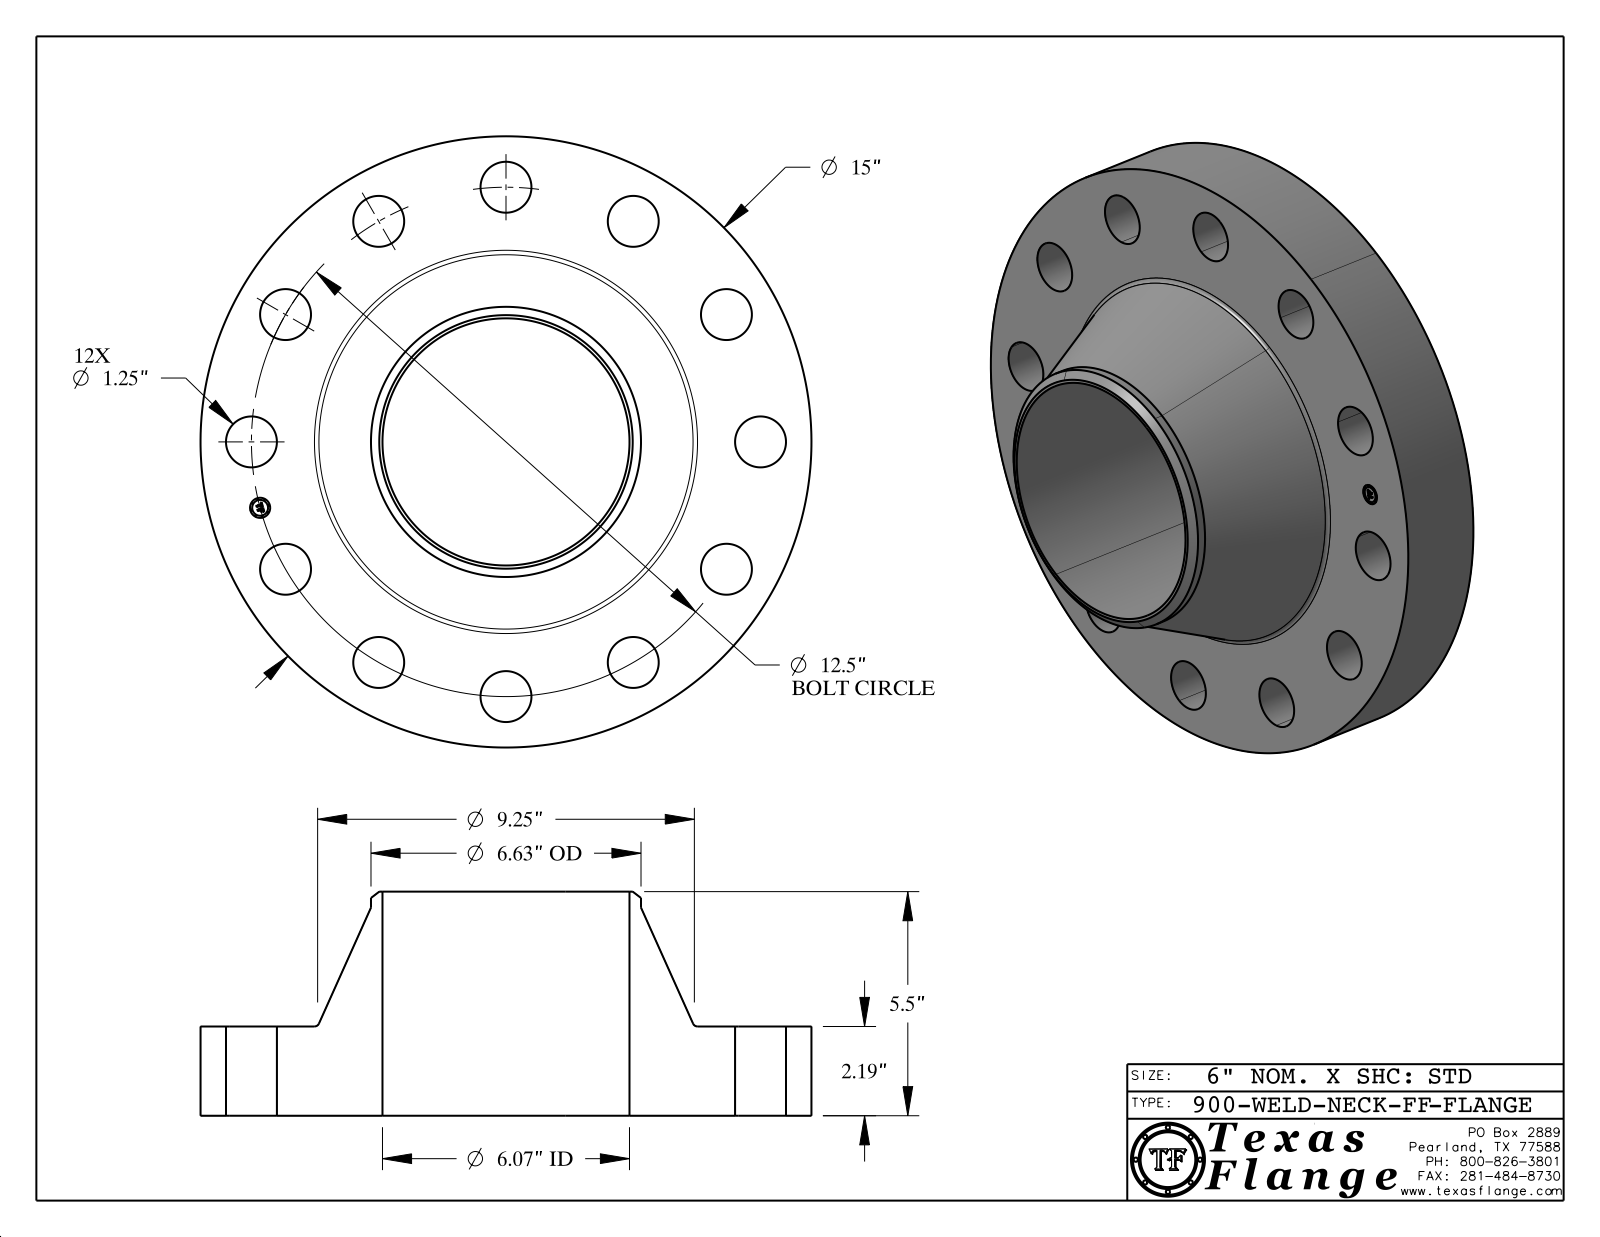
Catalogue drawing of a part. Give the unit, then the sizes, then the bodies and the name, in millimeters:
Units: millimetres
Overall size (bounding box): 381 × 381 × 139.7
Round holes (diameter × count): ⌀31.8 ×12, ⌀12.6 ×1, ⌀154.1 ×1
Round bosses / shafts (diameter × count): ⌀0.8 ×8, ⌀381 ×1, ⌀168.4 ×1, ⌀9.9 ×1
Main face-to-face distances: 55.6, 139.7, 84.1, 55.2, 0.4, 84.5, 3.8, 3.7, 0.7, 2.4
Hole centre spacings: 158.8, 224.5, 82.2, 275, 306.7, 317.5, 82.2, 158.8
Volume: 5 816 000 mm³ · Surface area: 406 500 mm²
Bodies: 1 solid, 424 faces (368 planar, 50 cylindrical, 6 other)
Part name (STEP PRODUCT): 900-WELD-NECK-FF
STEP written by: CATIA V5 STEP AP214 (AUTOMOTIVE_DESIGN)
